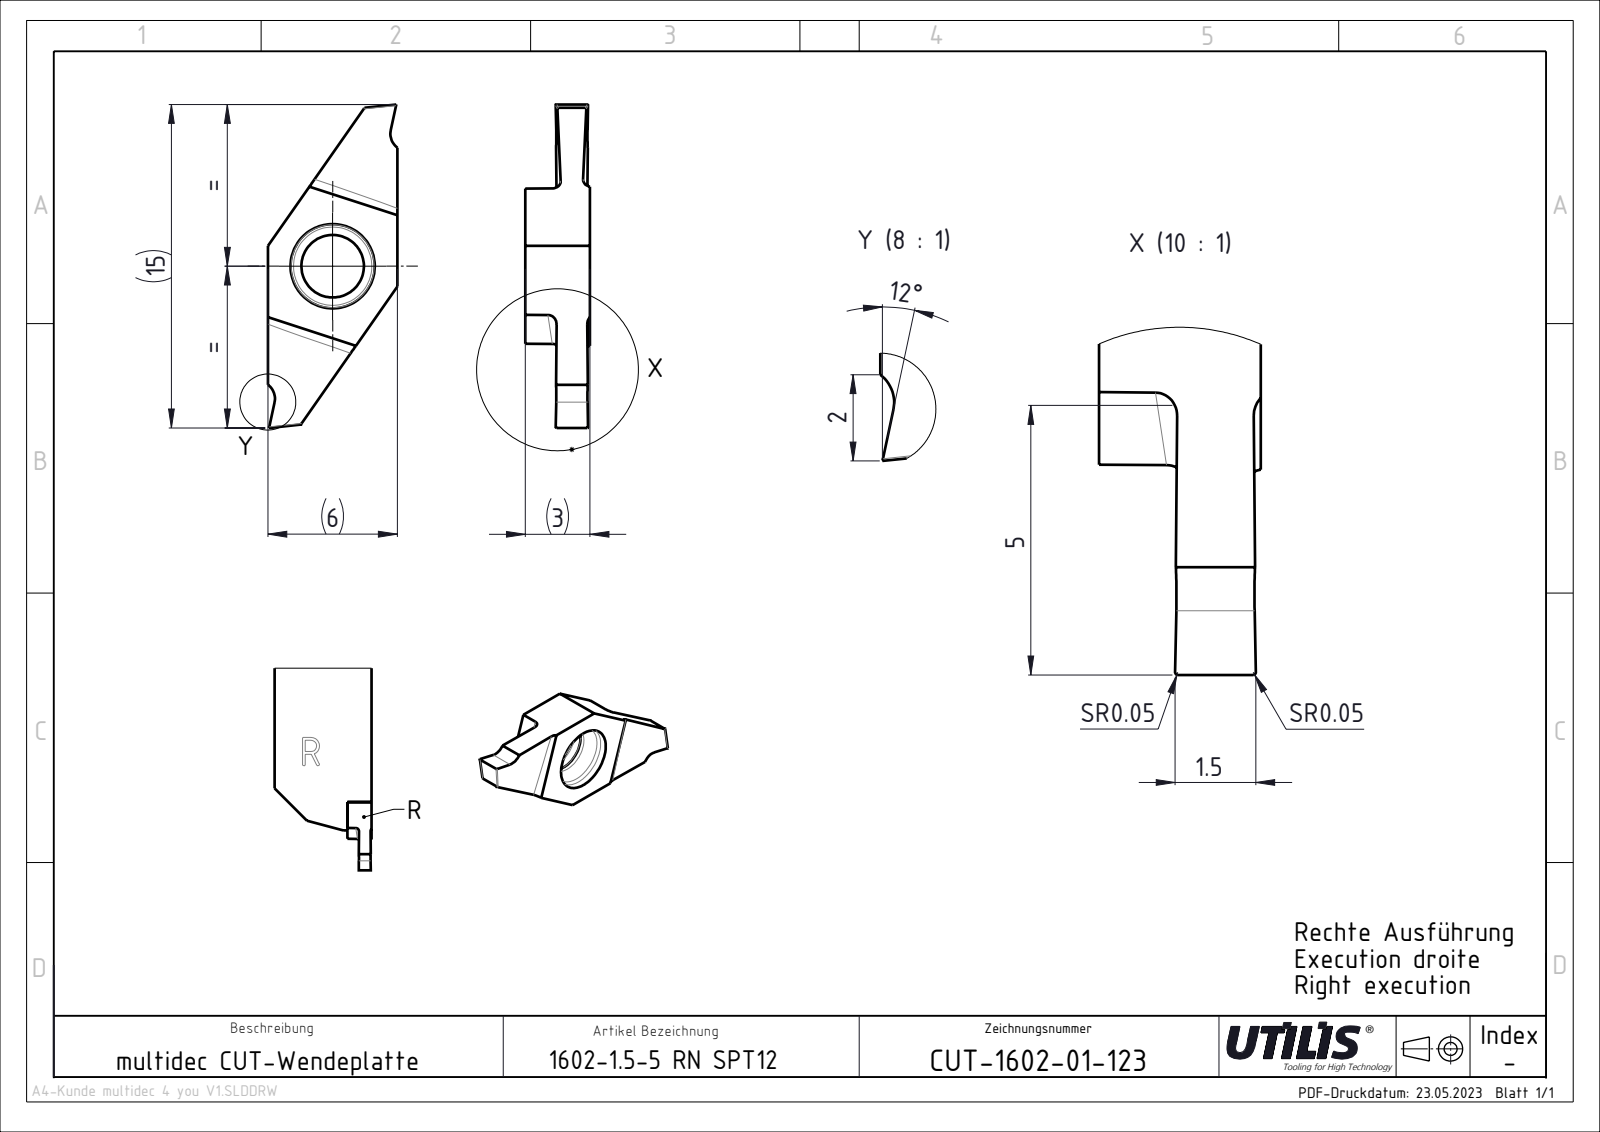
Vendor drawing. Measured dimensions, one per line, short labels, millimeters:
name: 1602-CUT-1602-01-123 stp
written by: SolidWorks 2022 (AUTOMOTIVE_DESIGN)
unit: mm
bodies: 1 solid, 23 faces (14 planar, 9 cylindrical, 0 other)
size: 15 × 6 × 3
volume: 118 mm³; area: 218 mm²
holes: 1× ⌀2.9
rounds: 4× R0.4
face distances: 6, 3, 1.34, 15
